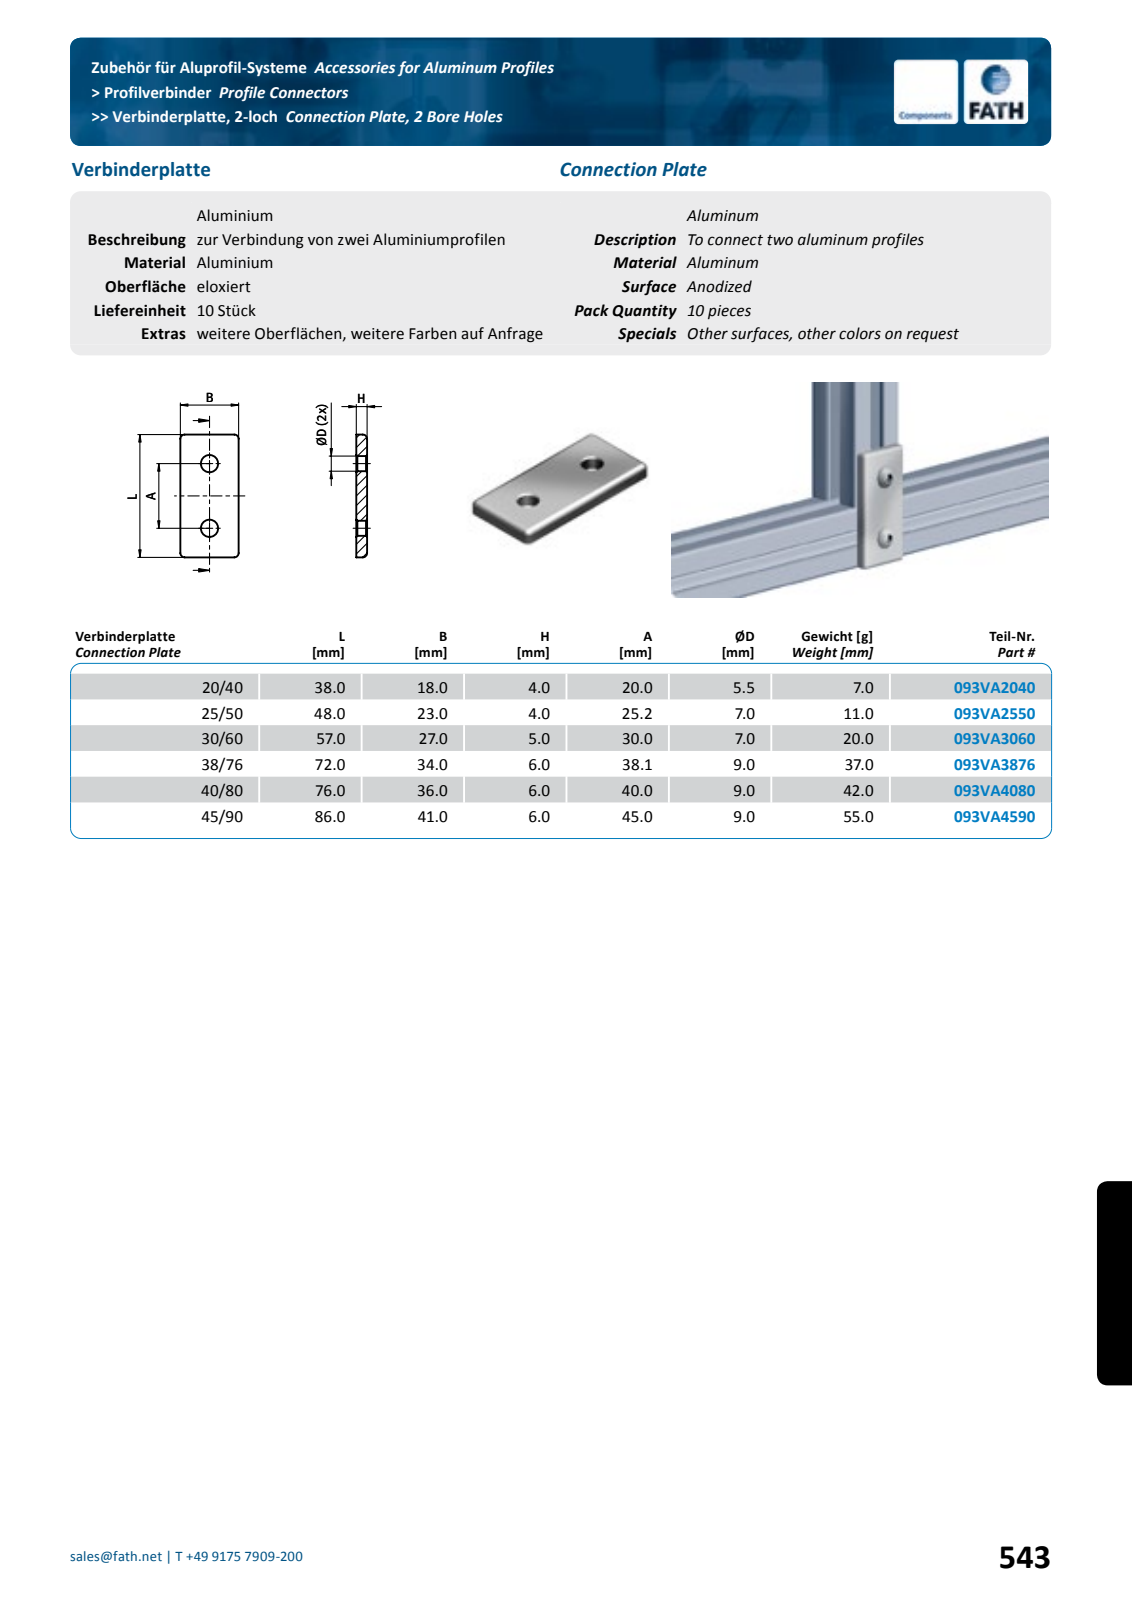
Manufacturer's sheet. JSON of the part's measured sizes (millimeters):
{"part_name": "fath_093va4590", "step_written_by": "Spatial InterOp 3D (automotive_design)", "units": "millimeters", "bodies": {"solids": 1, "faces": 30, "planar": 6, "cylindrical": 12, "other": 12}, "overall_size": [86, 41, 6], "volume_mm3": 20145, "surface_area_mm2": 8385, "round_holes": [[9, 2]], "partial_cylinders_radius": [[2, 8]], "face_to_face_distances": [6, 41, 86], "hole_center_spacings": [45]}
